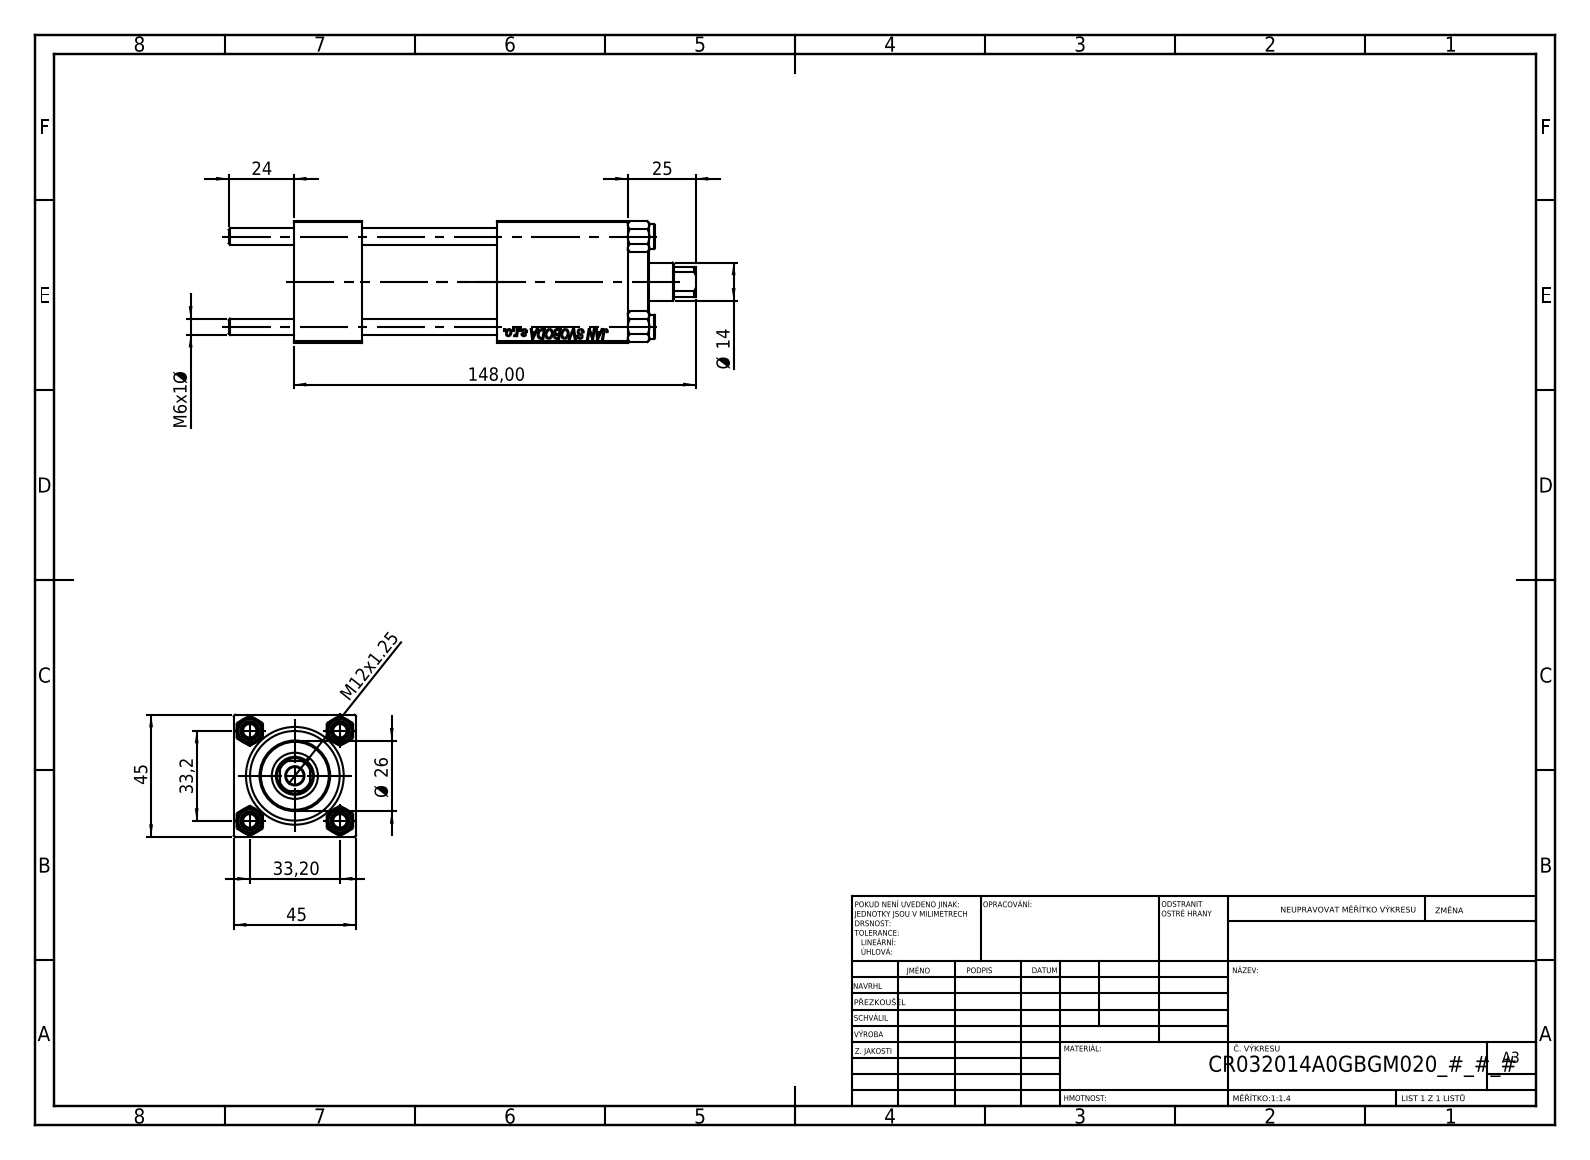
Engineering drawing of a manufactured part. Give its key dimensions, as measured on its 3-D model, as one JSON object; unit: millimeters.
{"part_name": "V215_VC_A; V215CR_VCP; CR025_012_A_0_G_A_G_M_020_+#_##_TYCINKA; V215CR_BODY_A (+1 more)", "step_written_by": "SolidWorks 2019 (CONFIG_CONTROL_DESIGN)", "units": "millimeters", "bodies": {"solids": 11, "faces": 1131, "planar": 517, "cylindrical": 78, "other": 536}, "overall_size": [172, 45, 45], "volume_mm3": 198558, "surface_area_mm2": 72750, "round_holes": [[6, 4], [7, 2], [13.16, 2], [20, 2], [6.5, 1], [14, 1], [17, 1], [24, 1], [32, 1], [33, 1]], "round_bosses_or_shafts": [[9, 4], [38, 1], [26, 1]], "partial_cylinders_radius": [[6.5, 1]], "face_to_face_distances": [45, 25, 123, 98, 50, 75, 48, 94.3, 69.3, 19.3], "hole_center_spacings": [23.48, 33.2, 46.95, 75.5]}
